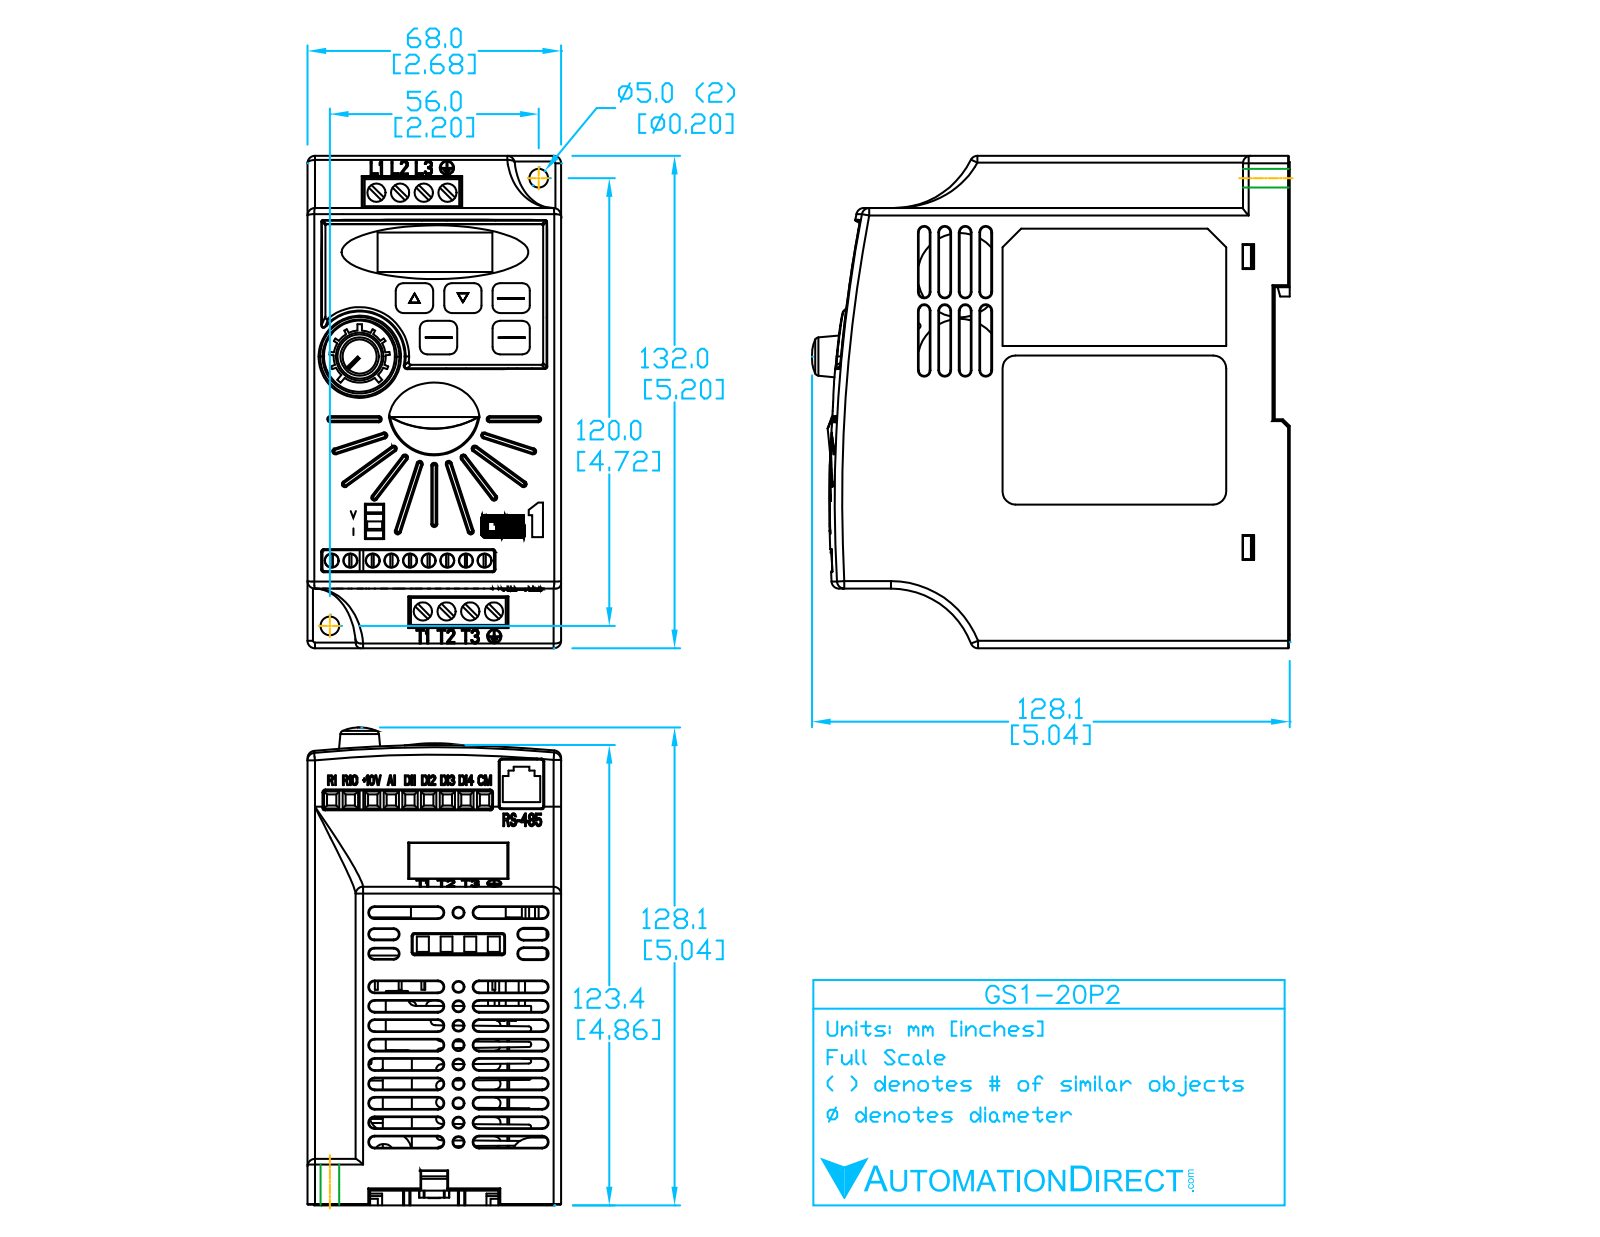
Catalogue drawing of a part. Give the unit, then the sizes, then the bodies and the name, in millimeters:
Units: millimetres
Overall size (bounding box): 134.2 × 132.1 × 68.1
Round holes (diameter × count): ⌀3.8 ×9, ⌀4.7 ×8, ⌀5.1 ×2
Round bosses / shafts (diameter × count): ⌀8 ×5
Partial cylindrical surfaces — rounded edges, fillets, slot ends (radius × count): R0.8 ×38, R2.5 ×22, R1.5 ×20, R1.6 ×6, R0.4 ×2, R2.4 ×2, R5.1 ×2, R11.2 ×2
Main face-to-face distances: 68.1, 4.4, 132.1, 0.4, 131.7, 4.2, 14, 118.1, 13.6, 15.7
Hole centre spacings: 5.1, 10.2, 15.2, 20.3, 25.4, 30.5, 35.6, 99.6
Volume: 1 008 000 mm³ · Surface area: 70 650 mm²
Bodies: 1 solid, 915 faces (566 planar, 168 cylindrical, 181 other)
Part name (STEP PRODUCT): GS1-20P2
STEP written by: SolidWorks 2013 (AUTOMOTIVE_DESIGN)
